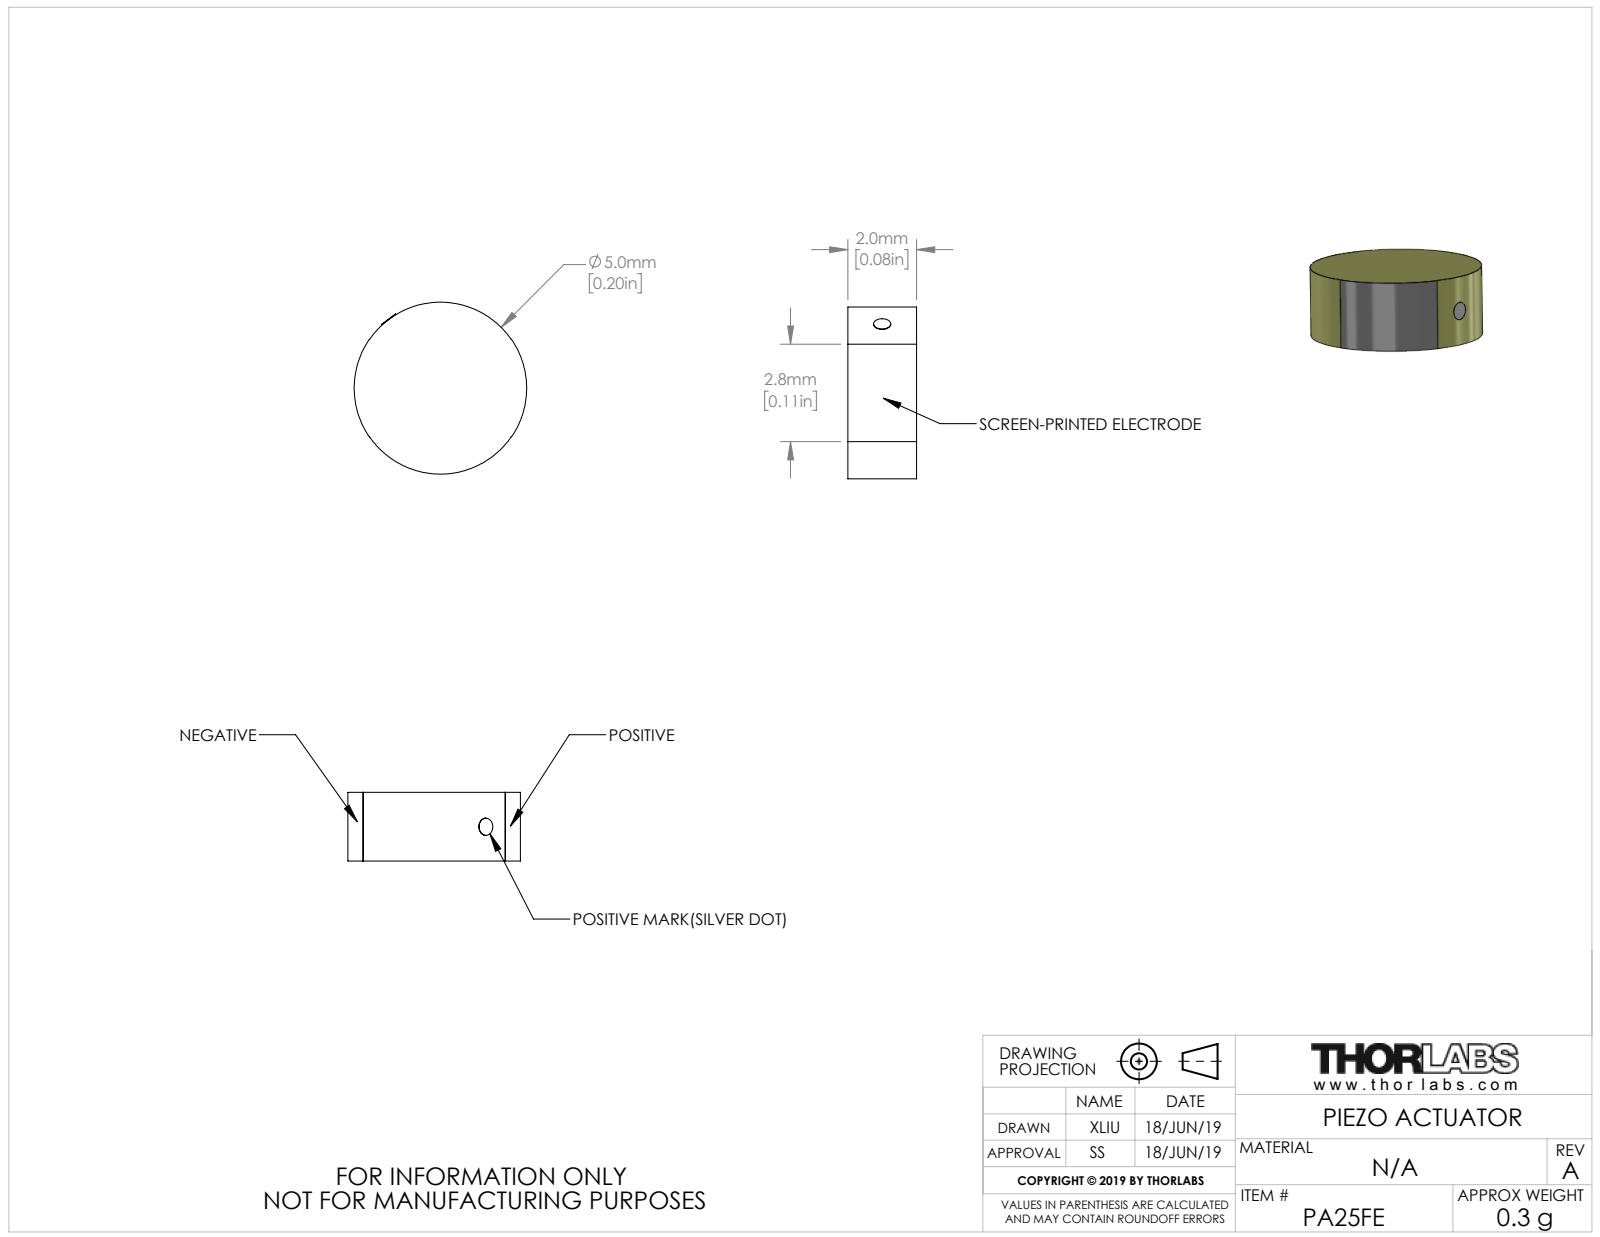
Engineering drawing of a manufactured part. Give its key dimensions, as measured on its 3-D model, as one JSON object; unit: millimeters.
{"part_name": "CTN014119", "step_written_by": "SolidWorks 2018 (AUTOMOTIVE_DESIGN)", "units": "millimeters", "bodies": {"solids": 2, "faces": 15, "planar": 8, "cylindrical": 7, "other": 0}, "overall_size": [5.02, 5, 2], "volume_mm3": 39, "surface_area_mm2": 71, "round_bosses_or_shafts": [[0.5, 1]], "partial_cylinders_radius": [[2.5, 1], [2.51, 1]], "face_to_face_distances": [2]}
